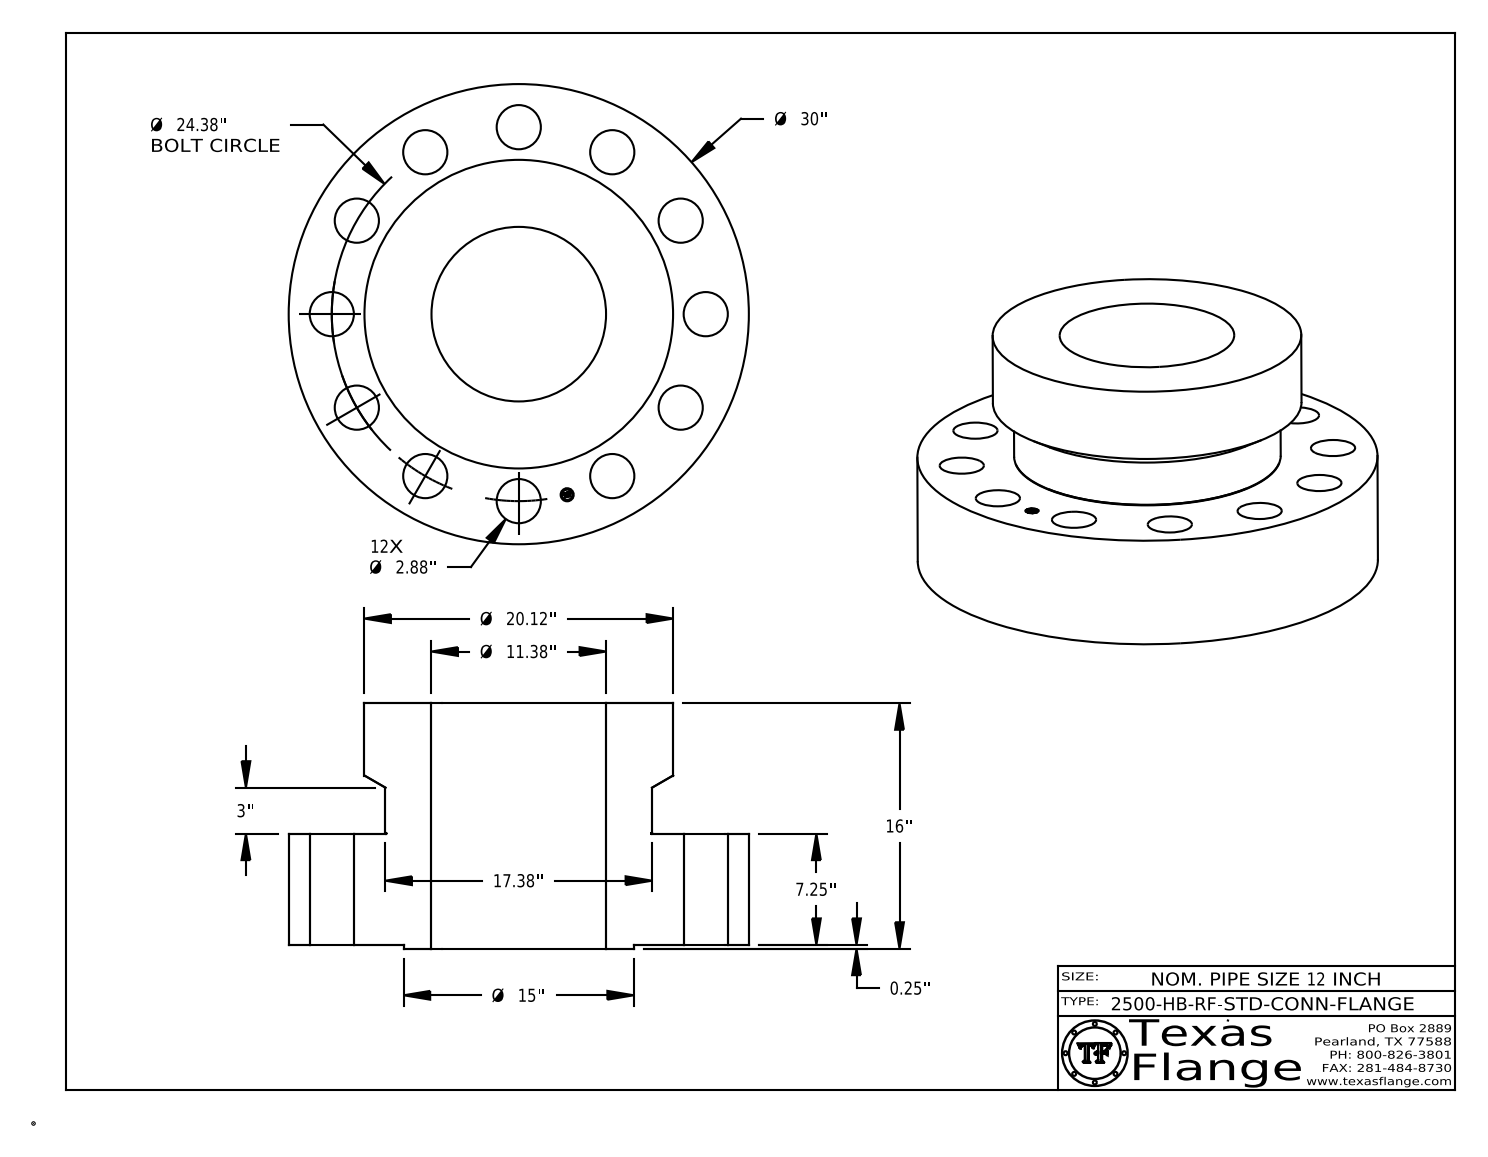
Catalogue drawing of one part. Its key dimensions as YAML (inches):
part_name: "12-2500-HB-RF-STD-CONN-FLANGE"
step_written_by: "CATIA V5 STEP AP214 (AUTOMOTIVE_DESIGN)"
units: inches
bodies: {solids: 1, faces: 429, planar: 369, cylindrical: 54, other: 6}
overall_size: [30, 30, 16]
volume: 5402
surface_area: 3746
round_holes:
  - {diameter: 2.88, count: 12}
  - {diameter: 0.85, count: 1}
  - {diameter: 11.38, count: 1}
round_bosses_or_shafts:
  - {diameter: 0.051, count: 8}
  - {diameter: 30, count: 1}
  - {diameter: 20.12, count: 1}
  - {diameter: 17.38, count: 1}
  - {diameter: 15, count: 1}
  - {diameter: 0.67, count: 1}
face_to_face_distances: [7.25, 15.75, 8.5, 0.25, 7.5, 16, 7.495, 7.245, 8.505, 0.254]
hole_center_spacings: [12.19, 6.31, 12.19, 17.239, 21.114, 23.549, 17.239, 21.113]
